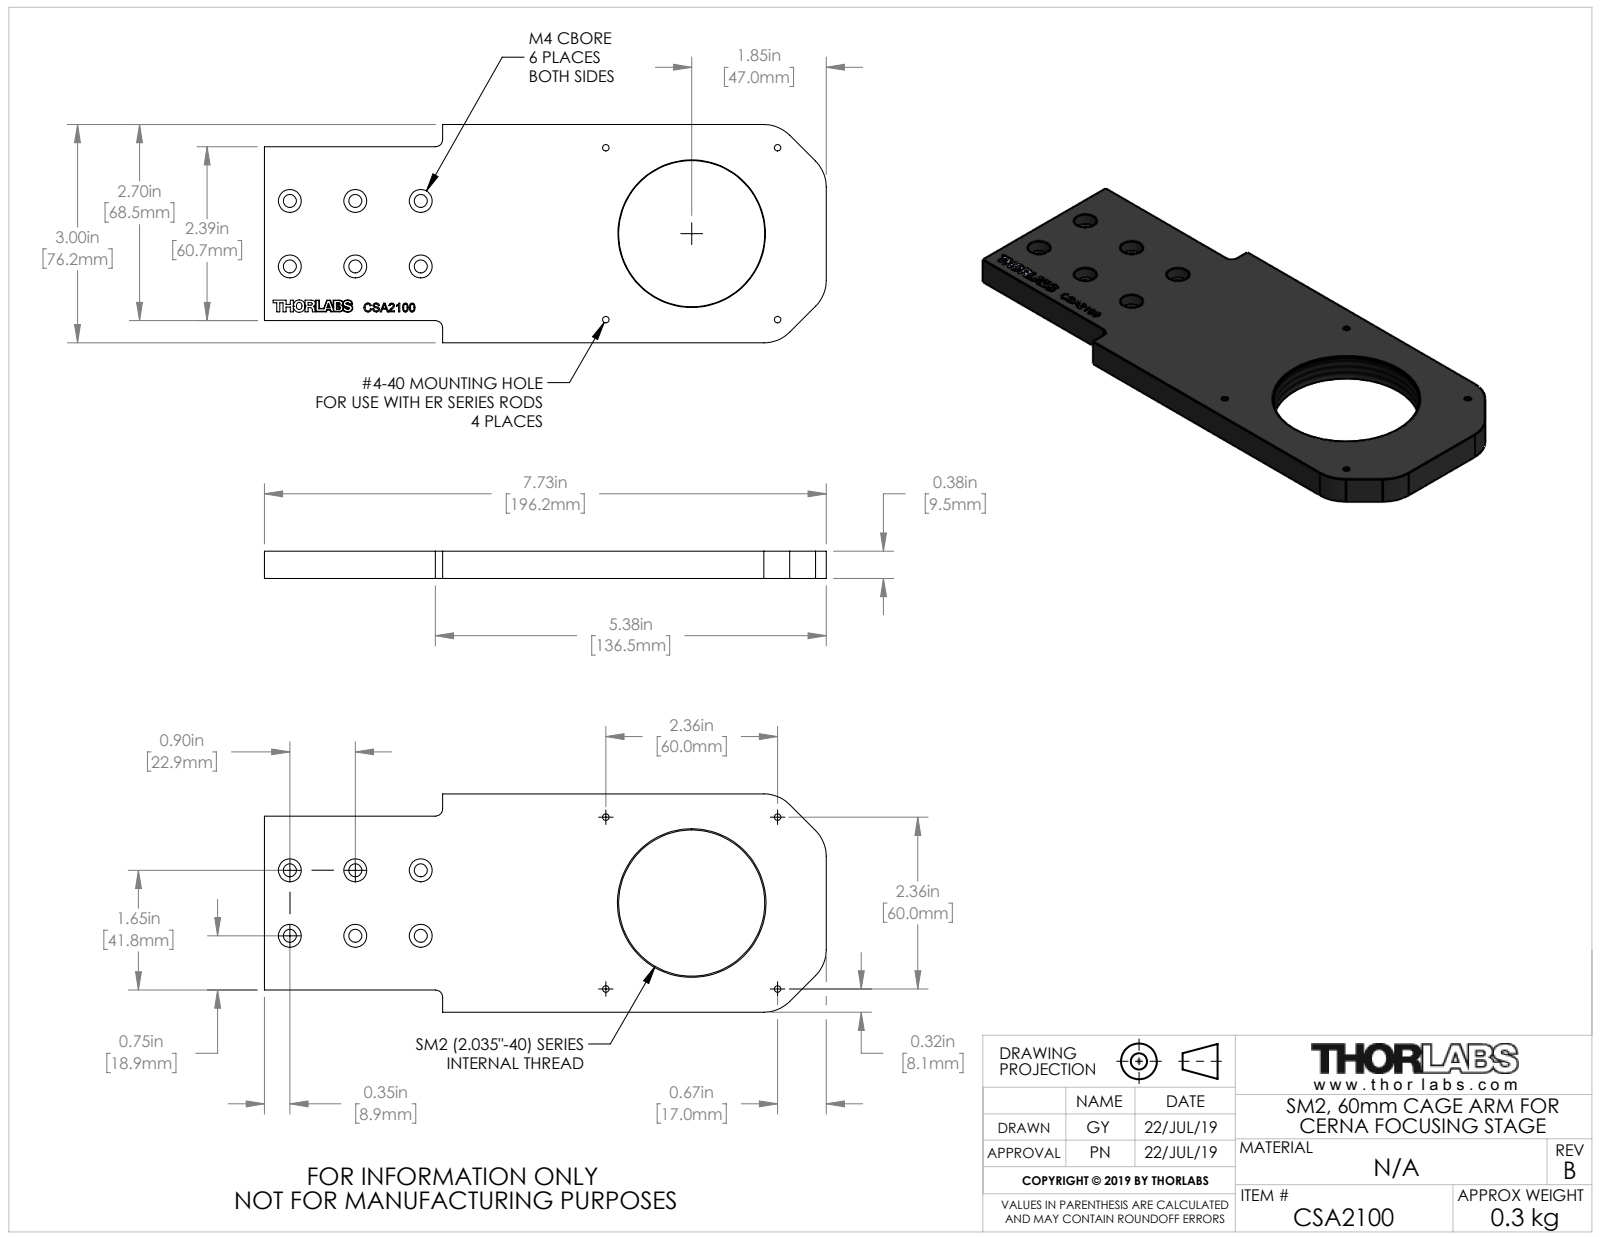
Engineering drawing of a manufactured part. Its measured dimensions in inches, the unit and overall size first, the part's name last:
Units: inches
Overall size (bounding box): 7.725 × 3 × 0.375
Round holes (diameter × count): ⌀0.177 ×6, ⌀0.315 ×6, ⌀0.089 ×4, ⌀2.008 ×1
Partial cylindrical surfaces — rounded edges, fillets, slot ends (radius × count): R0.5 ×4, R0.1 ×2
Main face-to-face distances: 0.375, 0.305, 2.695, 3, 2.39, 0.157, 0.218, 7.725, 0.06, 2.45
Hole centre spacings: 0.9, 1.273, 1.67, 2.362, 1.8, 2.013, 2.647, 3.022
Bodies: 0 solids, 103 faces (47 planar, 52 cylindrical, 4 other)
Part name (STEP PRODUCT): TTN042425-E0W
STEP written by: SolidWorks 2018 (AUTOMOTIVE_DESIGN)
